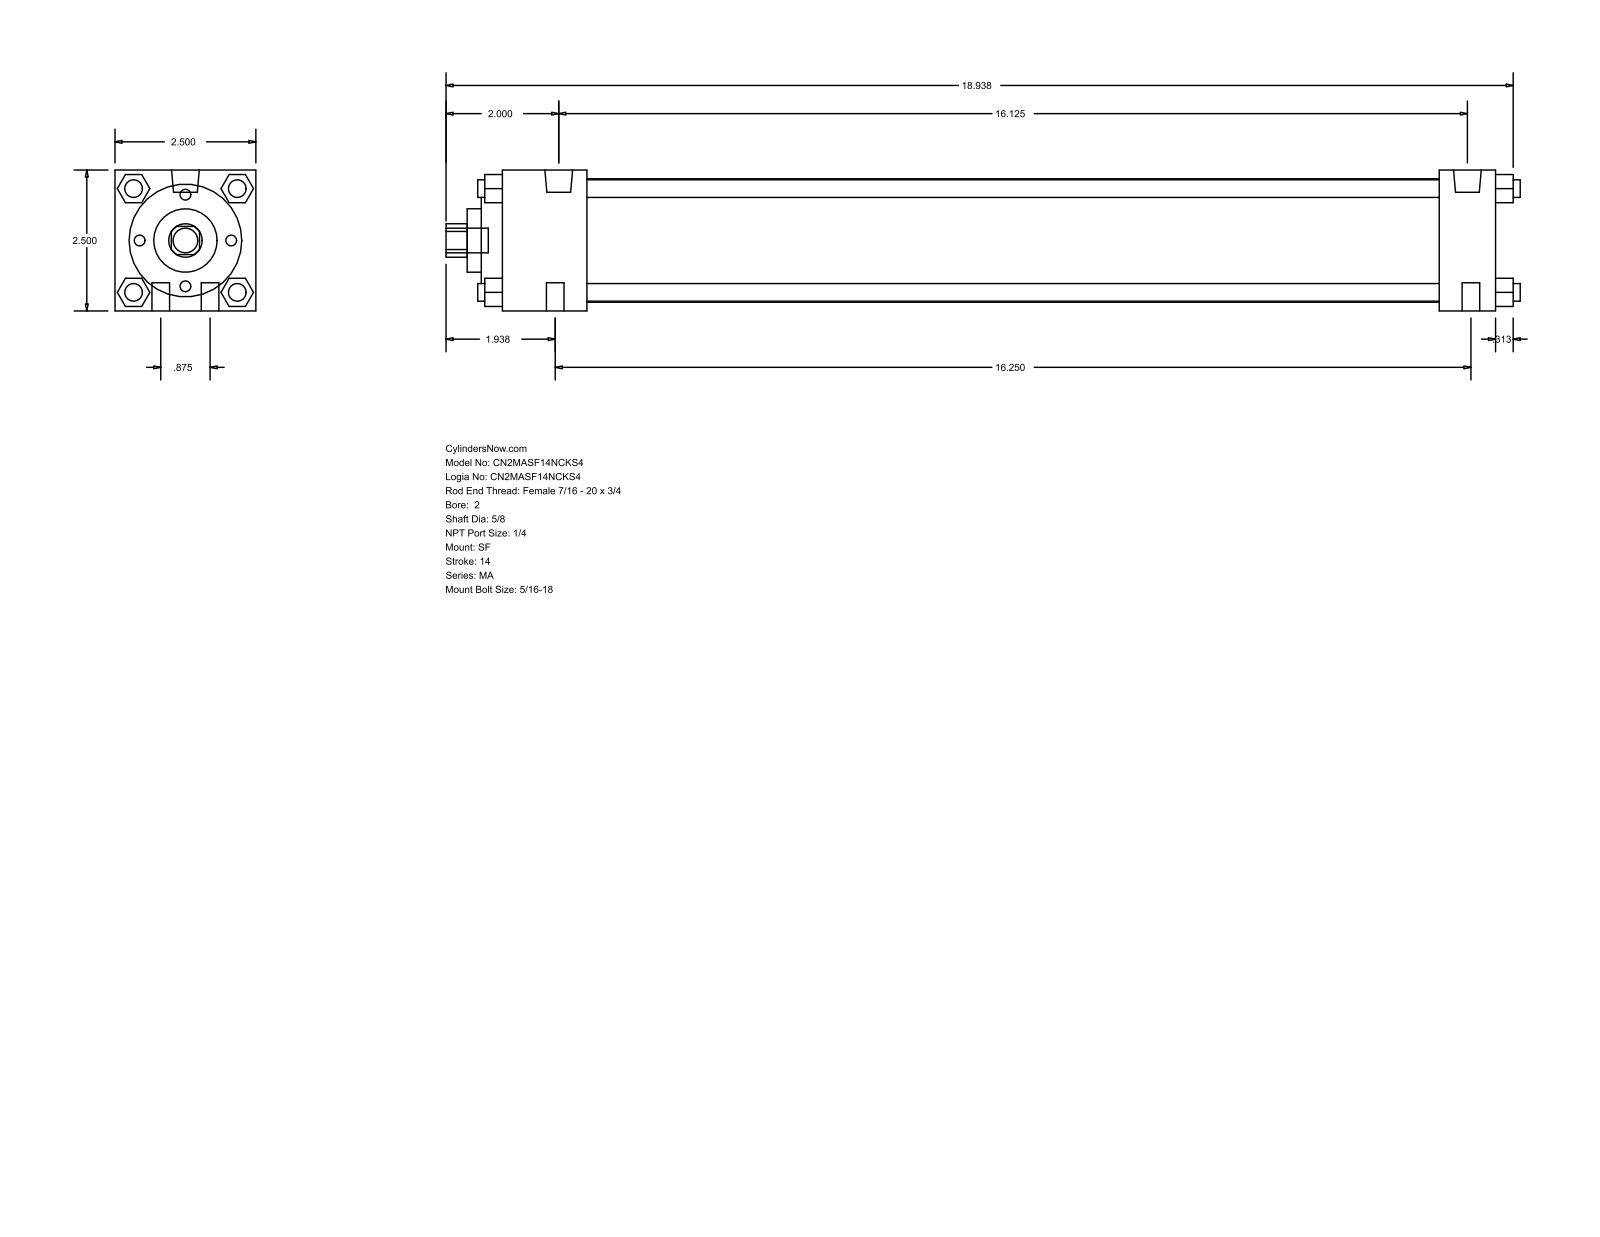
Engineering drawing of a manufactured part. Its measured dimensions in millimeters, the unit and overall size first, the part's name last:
Units: millimetres
Overall size (bounding box): 484.19 × 63.5 × 63.5
Round holes (diameter × count): ⌀15.88 ×1, ⌀28.57 ×1, ⌀50.8 ×1, ⌀55.63 ×1
Round bosses / shafts (diameter × count): ⌀7.94 ×10, ⌀12.49 ×2, ⌀11.11 ×1
Partial cylindrical surfaces — rounded edges, fillets, slot ends (radius × count): R7.54 ×1
Main face-to-face distances: 63.5, 12.7, 38.1, 9.52, 447.67, 422.28, 25.39, 384.18, 409.57, 47.62
Bodies: 0 solids, 126 faces (95 planar, 31 cylindrical, 0 other)
Part name (STEP PRODUCT): MA_SF__0200_0.625
STEP written by: GSSL Pune (CONFIG_CONTROL_DESIGN)
